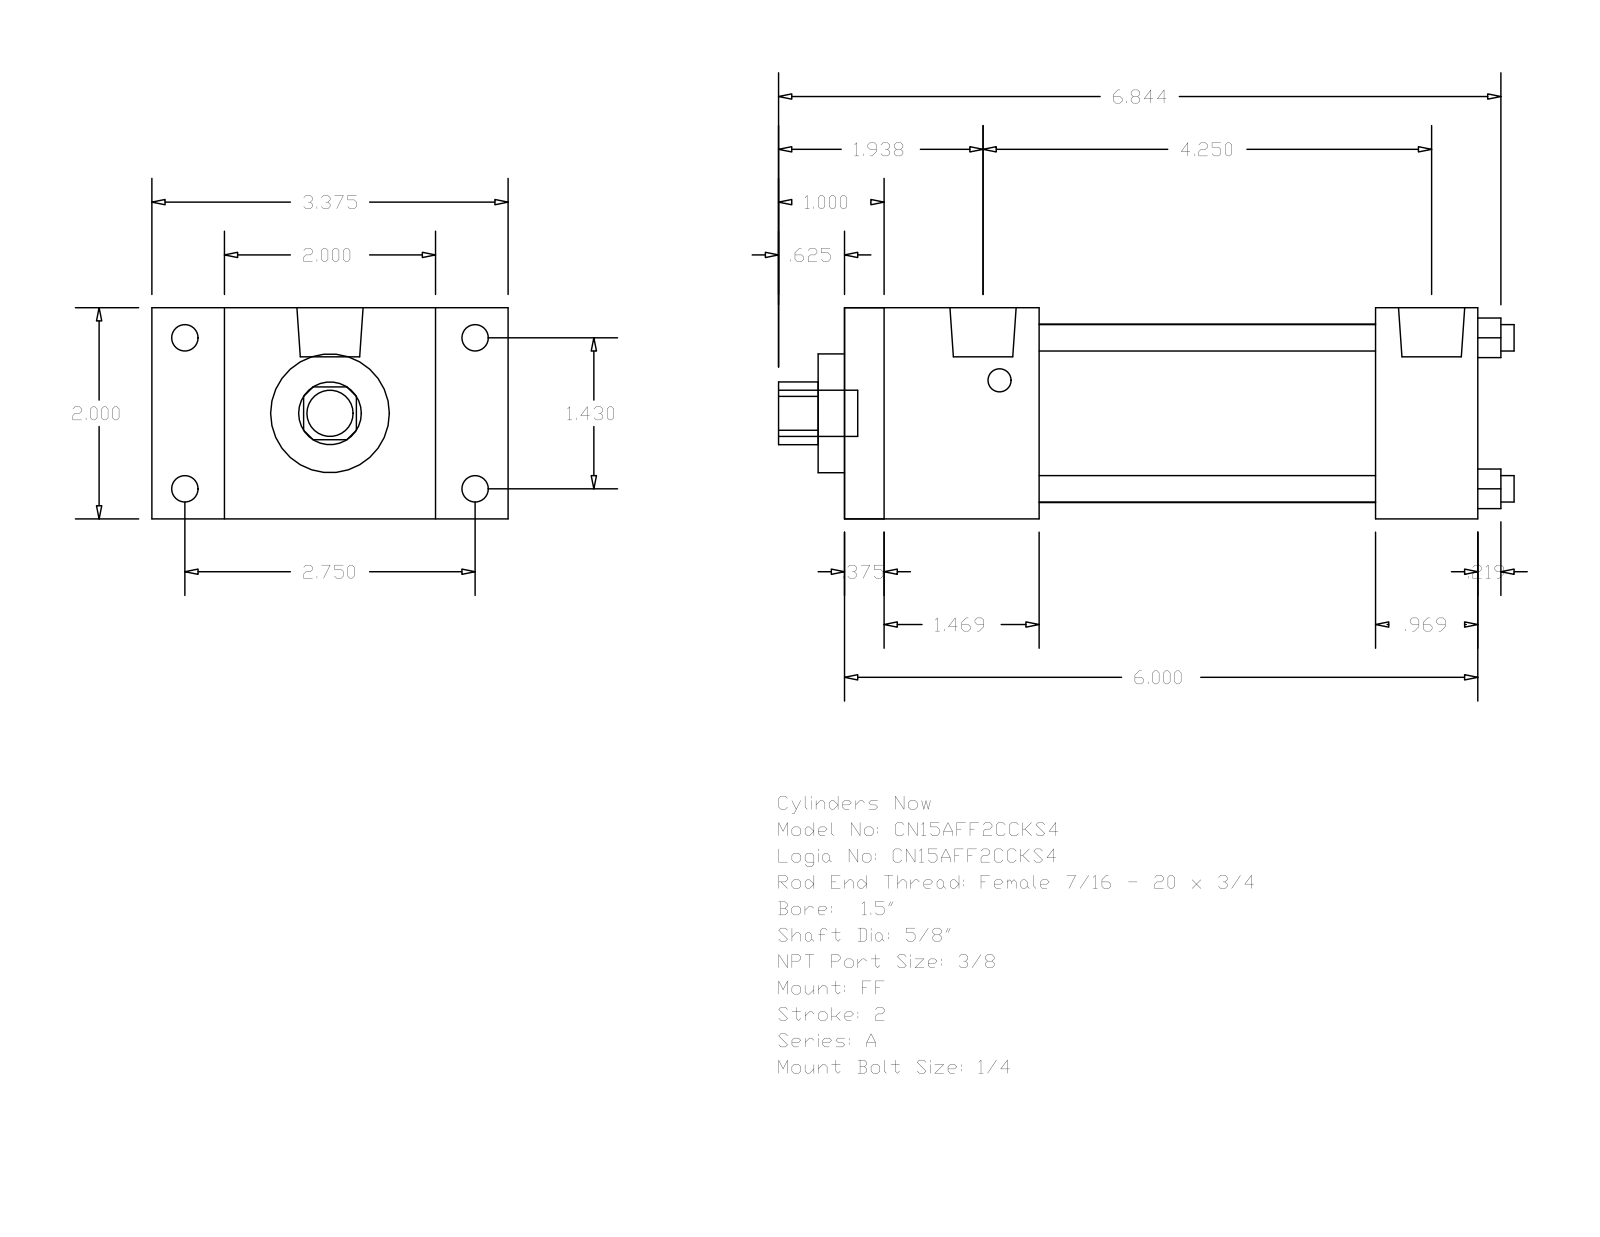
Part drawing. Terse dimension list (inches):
name: A_FF__0150_0.625
written by: GSSL Pune (CONFIG_CONTROL_DESIGN)
unit: in
bodies: 0 solids, 92 faces (64 planar, 28 cylindrical, 0 other)
size: 6.969 × 3.375 × 2
holes: 4× ⌀0.25, 1× ⌀0.625, 1× ⌀1.125, 1× ⌀1.69
bosses: 4× ⌀0.25, 4× ⌀0.219, 2× ⌀0.627, 1× ⌀0.437
rounds: 1× R0.297
face distances: 2, 6, 0.375, 5.625, 1.844, 5.031, 1.469, 4.656, 3.187, 4.156
hole spacings: 1.011, 1.43, 2.022
